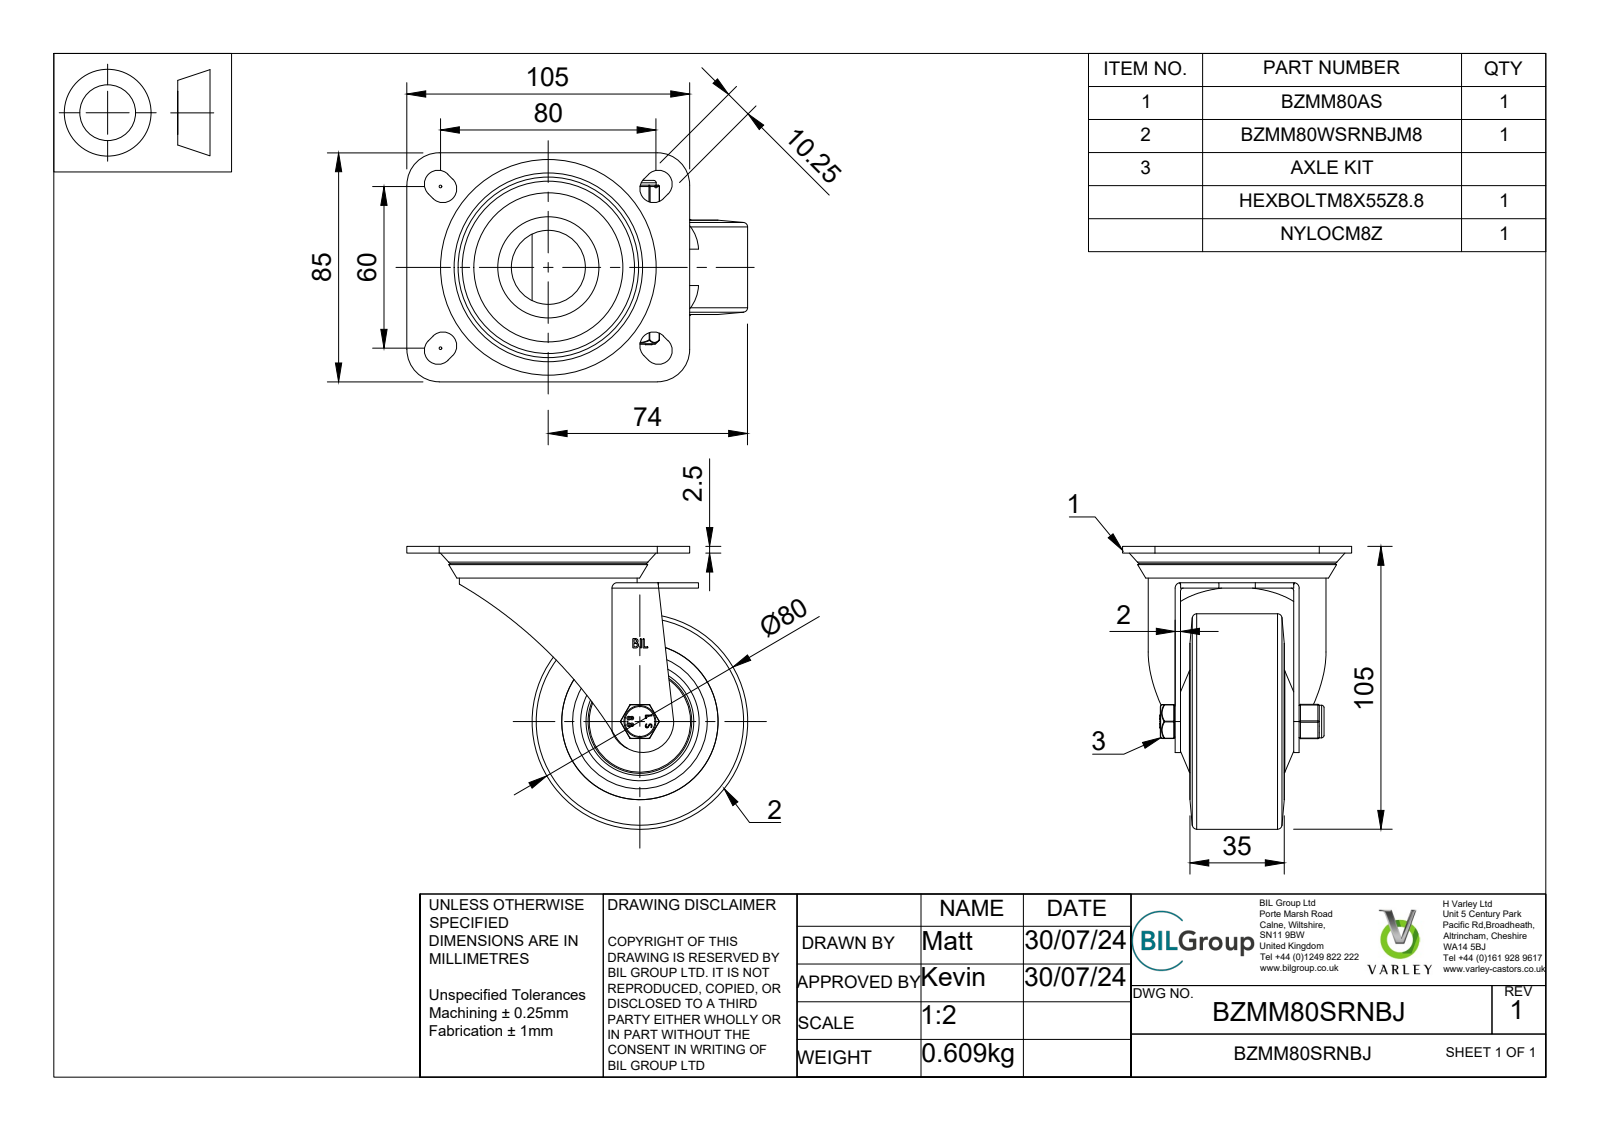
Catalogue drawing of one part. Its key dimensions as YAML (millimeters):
part_name: "BZMM80SRNBJ v3; BZMM80WSRNBJM8 v1; BZMH80WSRNBJ; ELASTIC RUBBER TYRE (+8 more)"
step_written_by: "Autodesk Translation Framework v13.14.0.145 (AUTOMOTIVE_DESIGN)"
units: millimeters
bodies: {solids: 47, faces: 754, planar: 267, cylindrical: 196, other: 291}
overall_size: [126.5, 105, 85]
volume: 204342
surface_area: 108193
round_holes:
  - {diameter: 0.66, count: 2}
  - {diameter: 8, count: 1}
  - {diameter: 8.2, count: 1}
  - {diameter: 8.6, count: 1}
  - {diameter: 15, count: 1}
  - {diameter: 20, count: 1}
  - {diameter: 22.5, count: 1}
  - {diameter: 26, count: 1}
  - {diameter: 27.5, count: 1}
  - {diameter: 30, count: 1}
  - {diameter: 31, count: 1}
  - {diameter: 32, count: 1}
round_bosses_or_shafts:
  - {diameter: 80, count: 1}
  - {diameter: 66, count: 1}
  - {diameter: 44, count: 1}
  - {diameter: 38.5, count: 1}
  - {diameter: 35, count: 1}
  - {diameter: 31.5, count: 1}
  - {diameter: 30.5, count: 1}
  - {diameter: 28, count: 1}
partial_cylinders:
  - {radius: 0.5, count: 18}
  - {radius: 0.25, count: 12}
  - {radius: 5.12, count: 8}
  - {radius: 12, count: 5}
  - {radius: 0.33, count: 4}
  - {radius: 0.64, count: 4}
  - {radius: 1, count: 4}
  - {radius: 0.63, count: 2}
face_to_face_distances: [2, 2.5, 8, 5.5, 10.5, 0.5, 44, 13.5, 10, 11]
hole_center_spacings: [3.22, 2.49]
